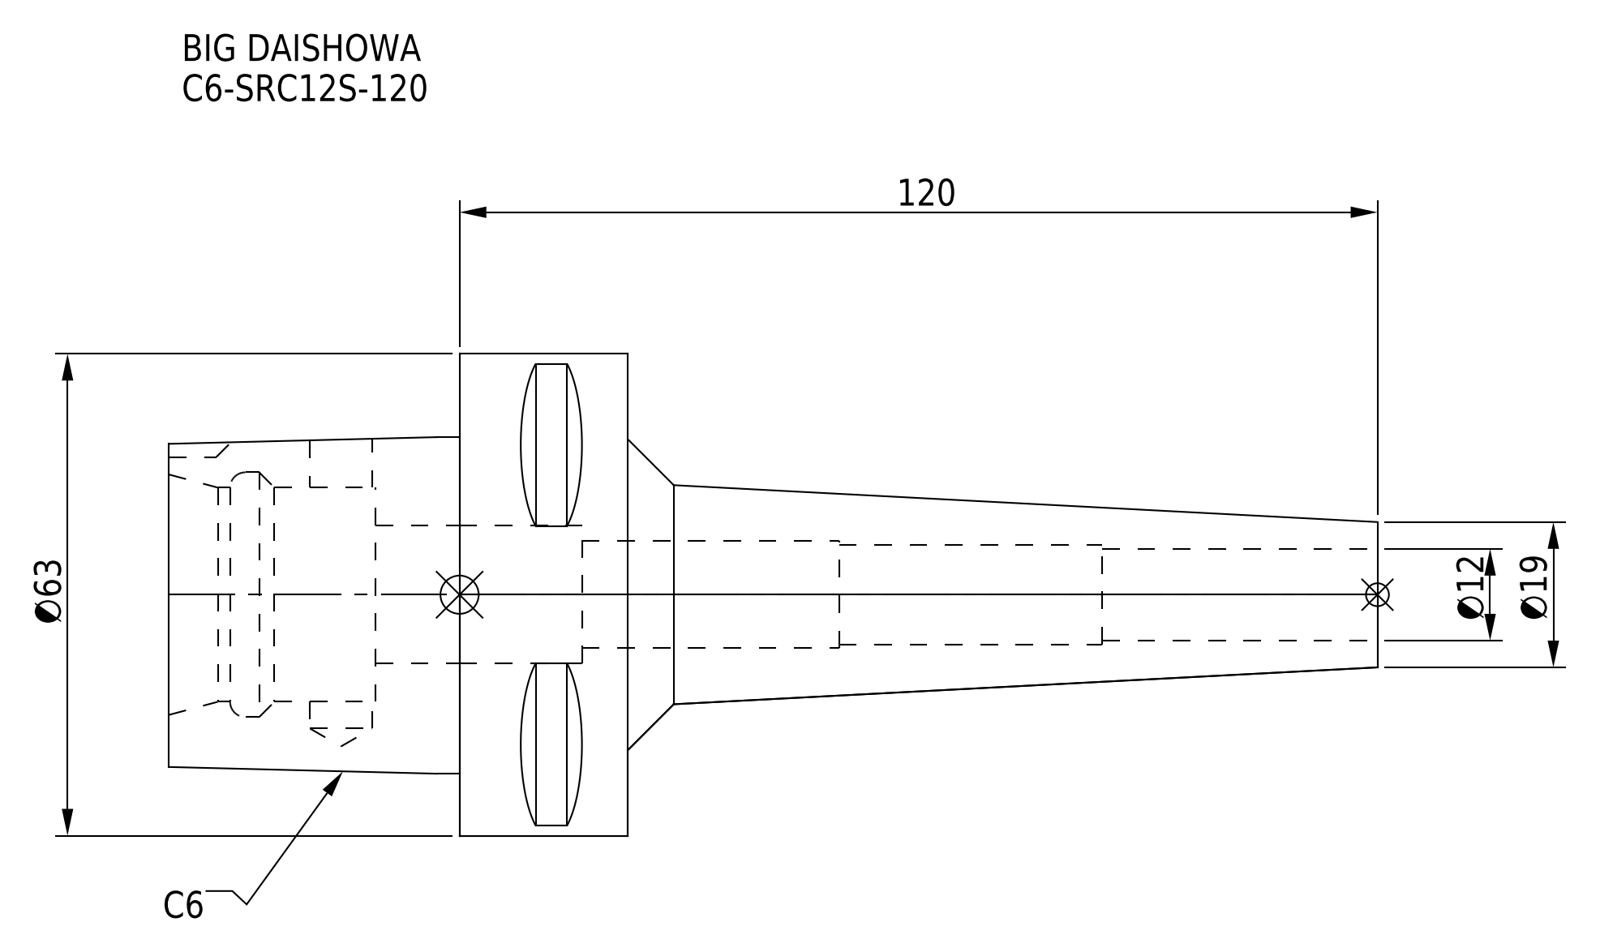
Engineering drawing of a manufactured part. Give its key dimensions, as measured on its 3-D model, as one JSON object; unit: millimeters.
{"part_name": "C6-SRC12S-120", "step_written_by": "CREO PARAMETRIC BY PTC INC, 2016380 (AUTOMOTIVE_DESIGN)", "units": "millimeters", "bodies": {"solids": 1, "faces": 65, "planar": 30, "cylindrical": 21, "other": 14}, "overall_size": [158, 63, 63], "volume_mm3": 130049, "surface_area_mm2": 30967, "round_holes": [[8.1, 1], [12, 1], [13, 1], [14, 1], [18, 1], [28, 1], [32, 1]], "round_bosses_or_shafts": [[63, 1]], "partial_cylinders_radius": [[5, 1]], "face_to_face_distances": [22, 60, 38, 27, 33, 11, 24.89, 55.4, 98, 120]}
